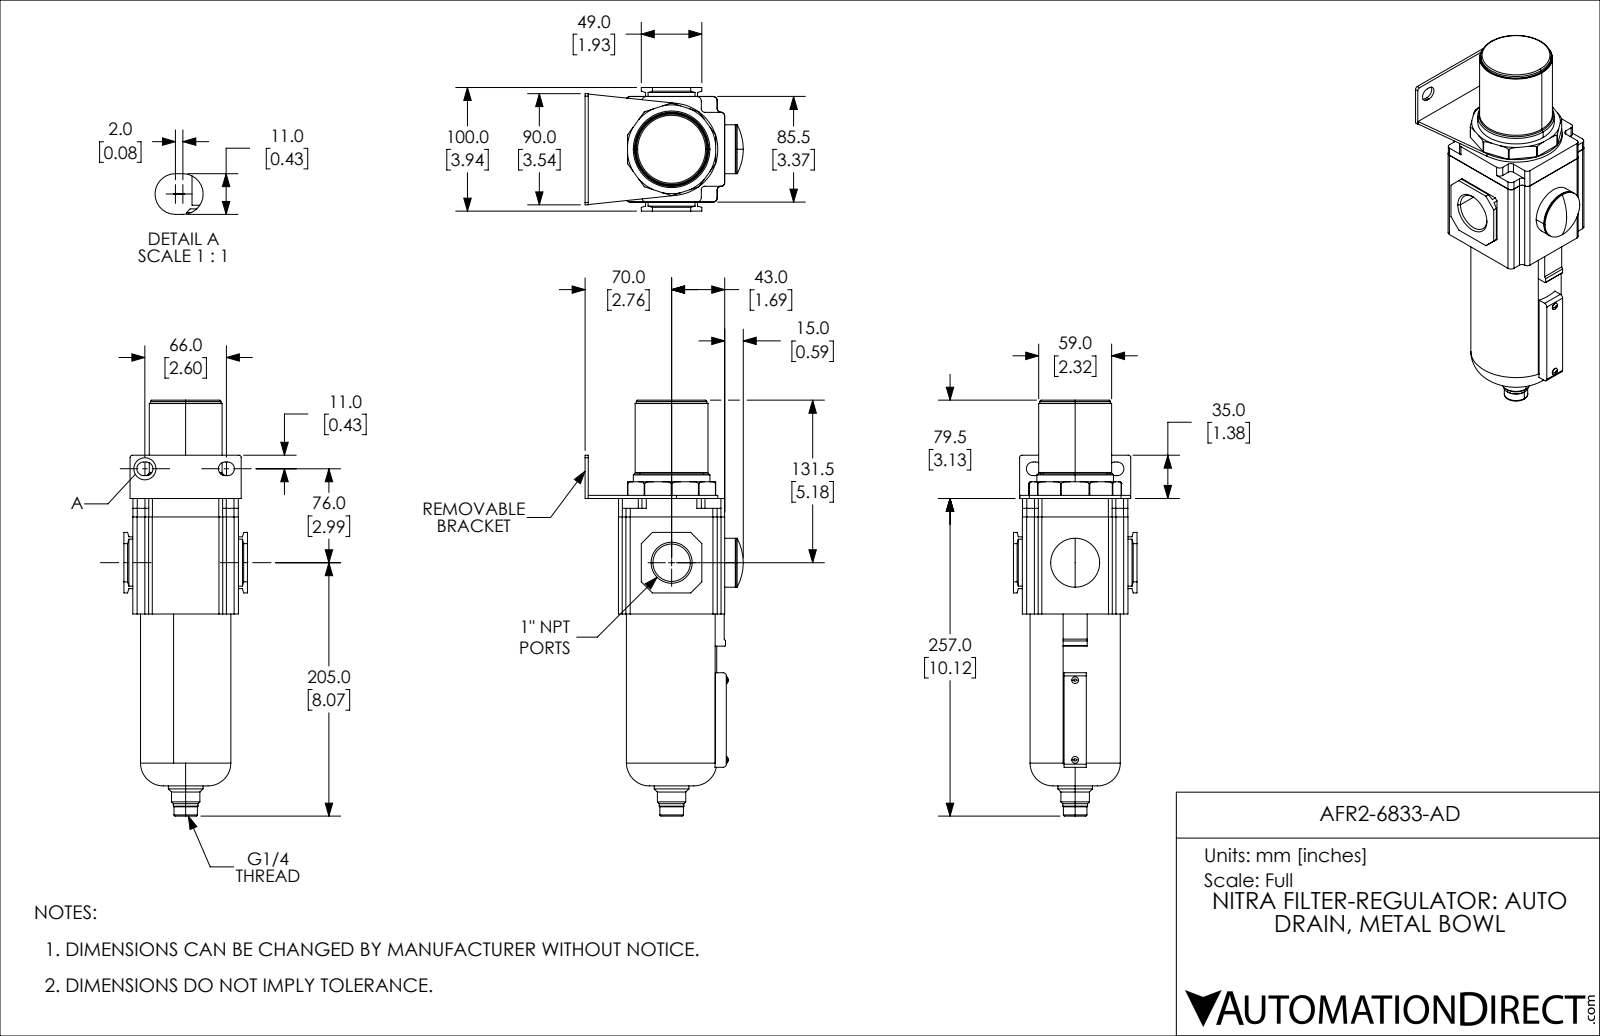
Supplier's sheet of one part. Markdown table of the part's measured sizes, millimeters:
| quantity | value |
| --- | --- |
| part name | AFR2-6833-AD |
| STEP written by | SolidWorks 2019 (CONFIG_CONTROL_DESIGN) |
| units | millimeters |
| bodies | 1 solid, 235 faces (116 planar, 79 cylindrical, 40 other) |
| overall size | 336.5 × 128 × 100 |
| volume | 1 494 000 mm³ |
| surface area | 118 095 mm² |
| round holes (diameter × count) | 11.45 × 1, 30.29 × 1 |
| round bosses / shafts (diameter × count) | 5.5 × 2, 73.1 × 1, 62 × 1, 59 × 1, 57 × 1, 51.4 × 1, 39.6 × 1, 28 × 1 |
| partial cylindrical surfaces (radius × count) | 3 × 20, 3.5 × 12, 5.5 × 4, 2 × 2, 2.5 × 2, 37.4 × 1 |
| main face-to-face distances | 2.5, 85.5, 86, 110.5, 27, 113, 7.25, 92.75, 93.5, 96 |
